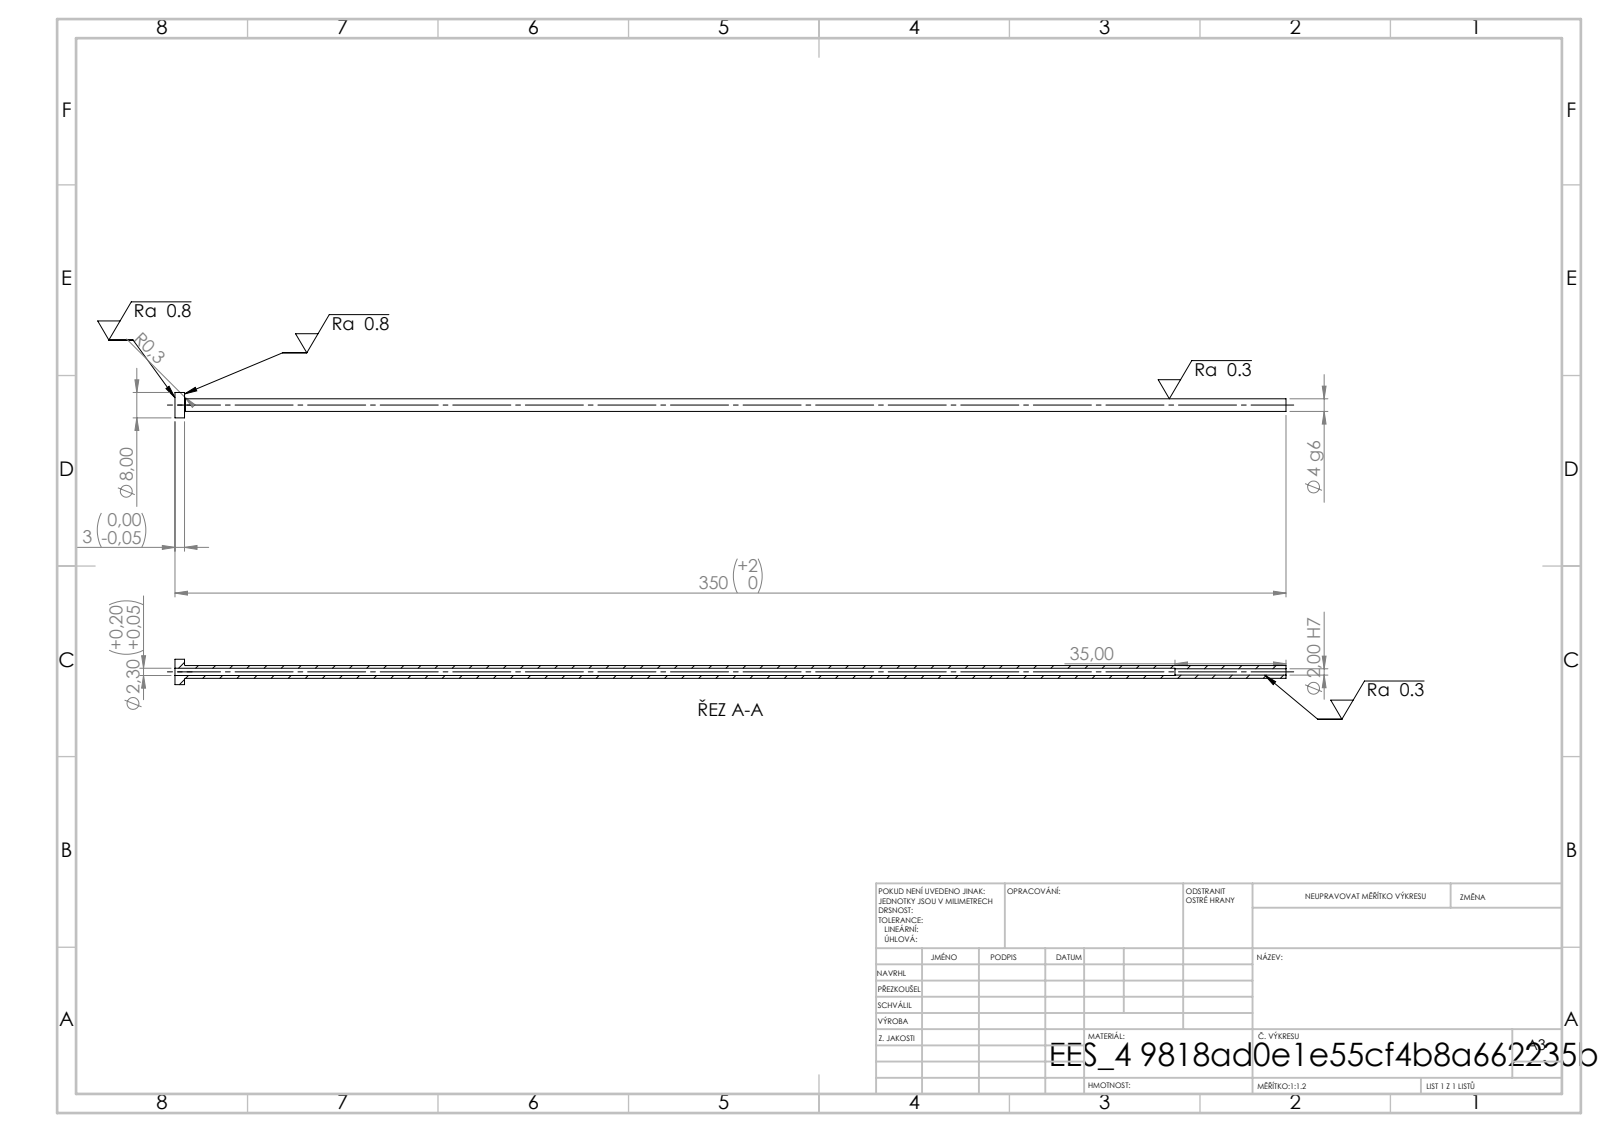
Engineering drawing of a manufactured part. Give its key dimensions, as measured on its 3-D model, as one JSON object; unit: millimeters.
{"step_written_by": "SolidWorks 2019 (CONFIG_CONTROL_DESIGN)", "units": "millimeters", "bodies": {"solids": 1, "faces": 14, "planar": 4, "cylindrical": 8, "other": 2}, "overall_size": [350, 8, 8], "volume_mm3": 3093, "surface_area_mm2": 7025, "round_holes": [[2, 1], [2.3, 1]], "round_bosses_or_shafts": [[8, 1], [4, 1]], "face_to_face_distances": [3, 350, 347, 315, 312, 35]}
